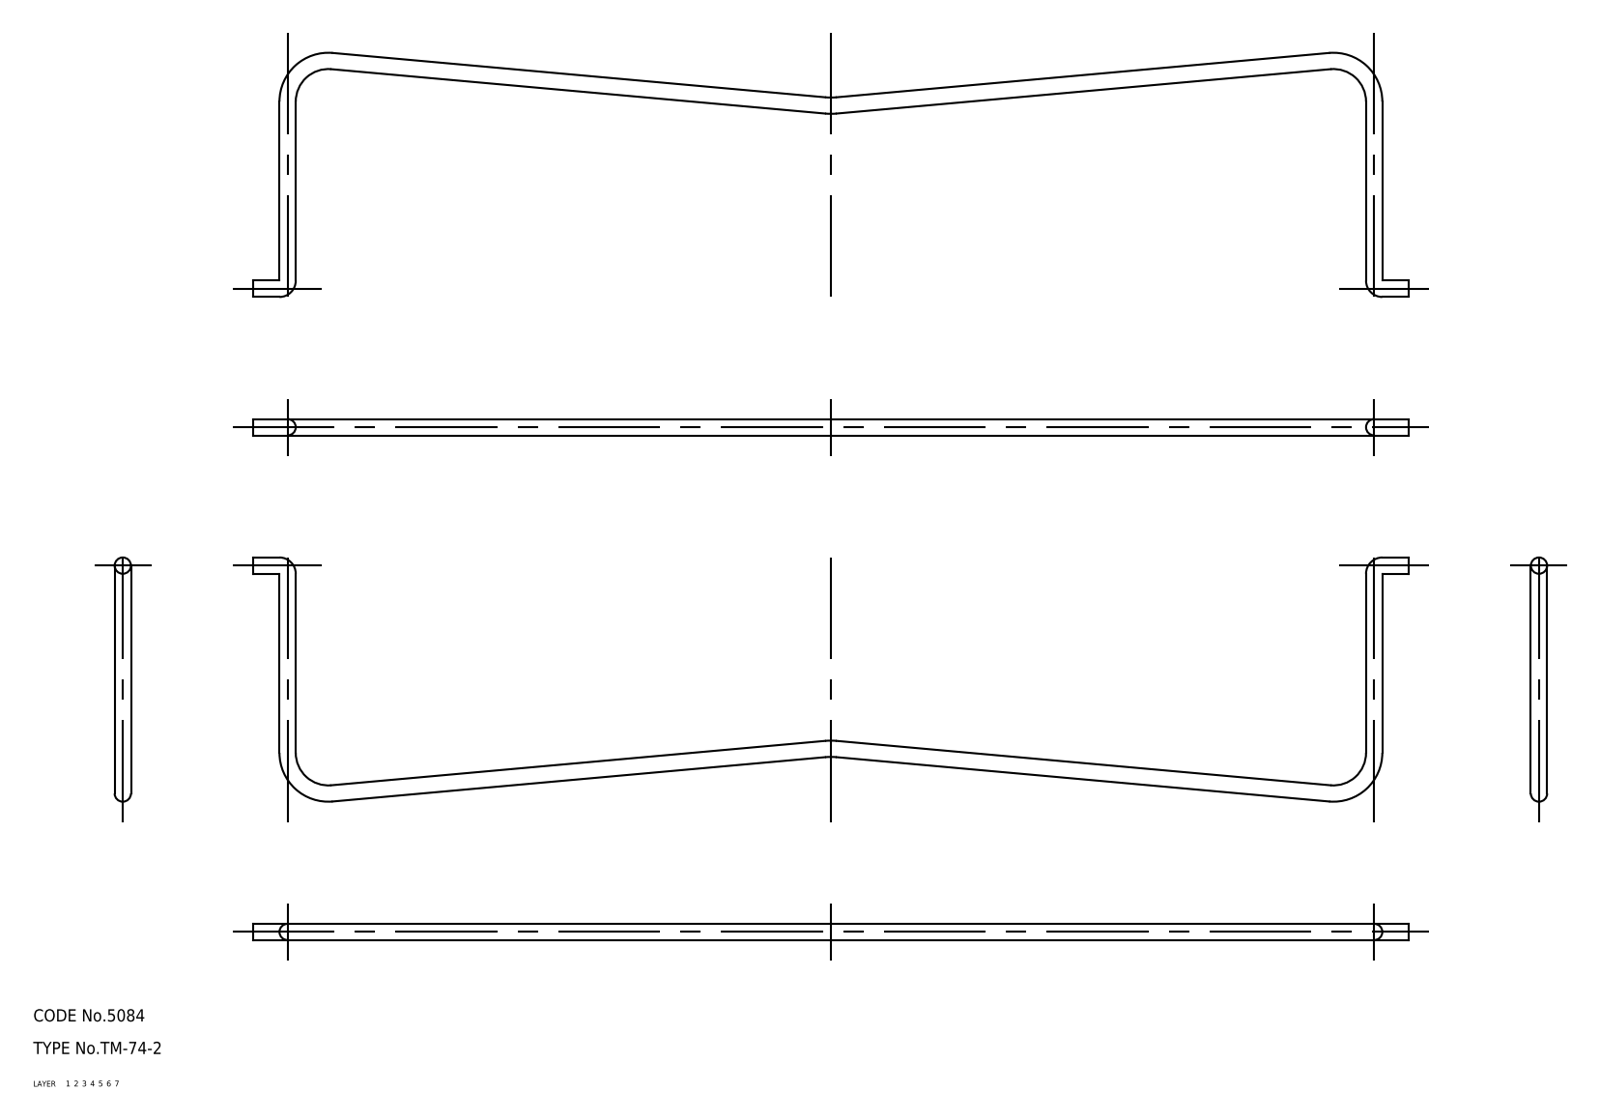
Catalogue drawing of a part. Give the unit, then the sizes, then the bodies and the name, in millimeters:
Units: millimetres
Overall size (bounding box): 284 × 60 × 4
Volume: 4 797 mm³ · Surface area: 4 885 mm²
Bodies: 1 solid, 24 faces (0 planar, 0 cylindrical, 24 other)
Part name (STEP PRODUCT): stand
STEP written by: CADfix (AUTOMOTIVE_DESIGN)
